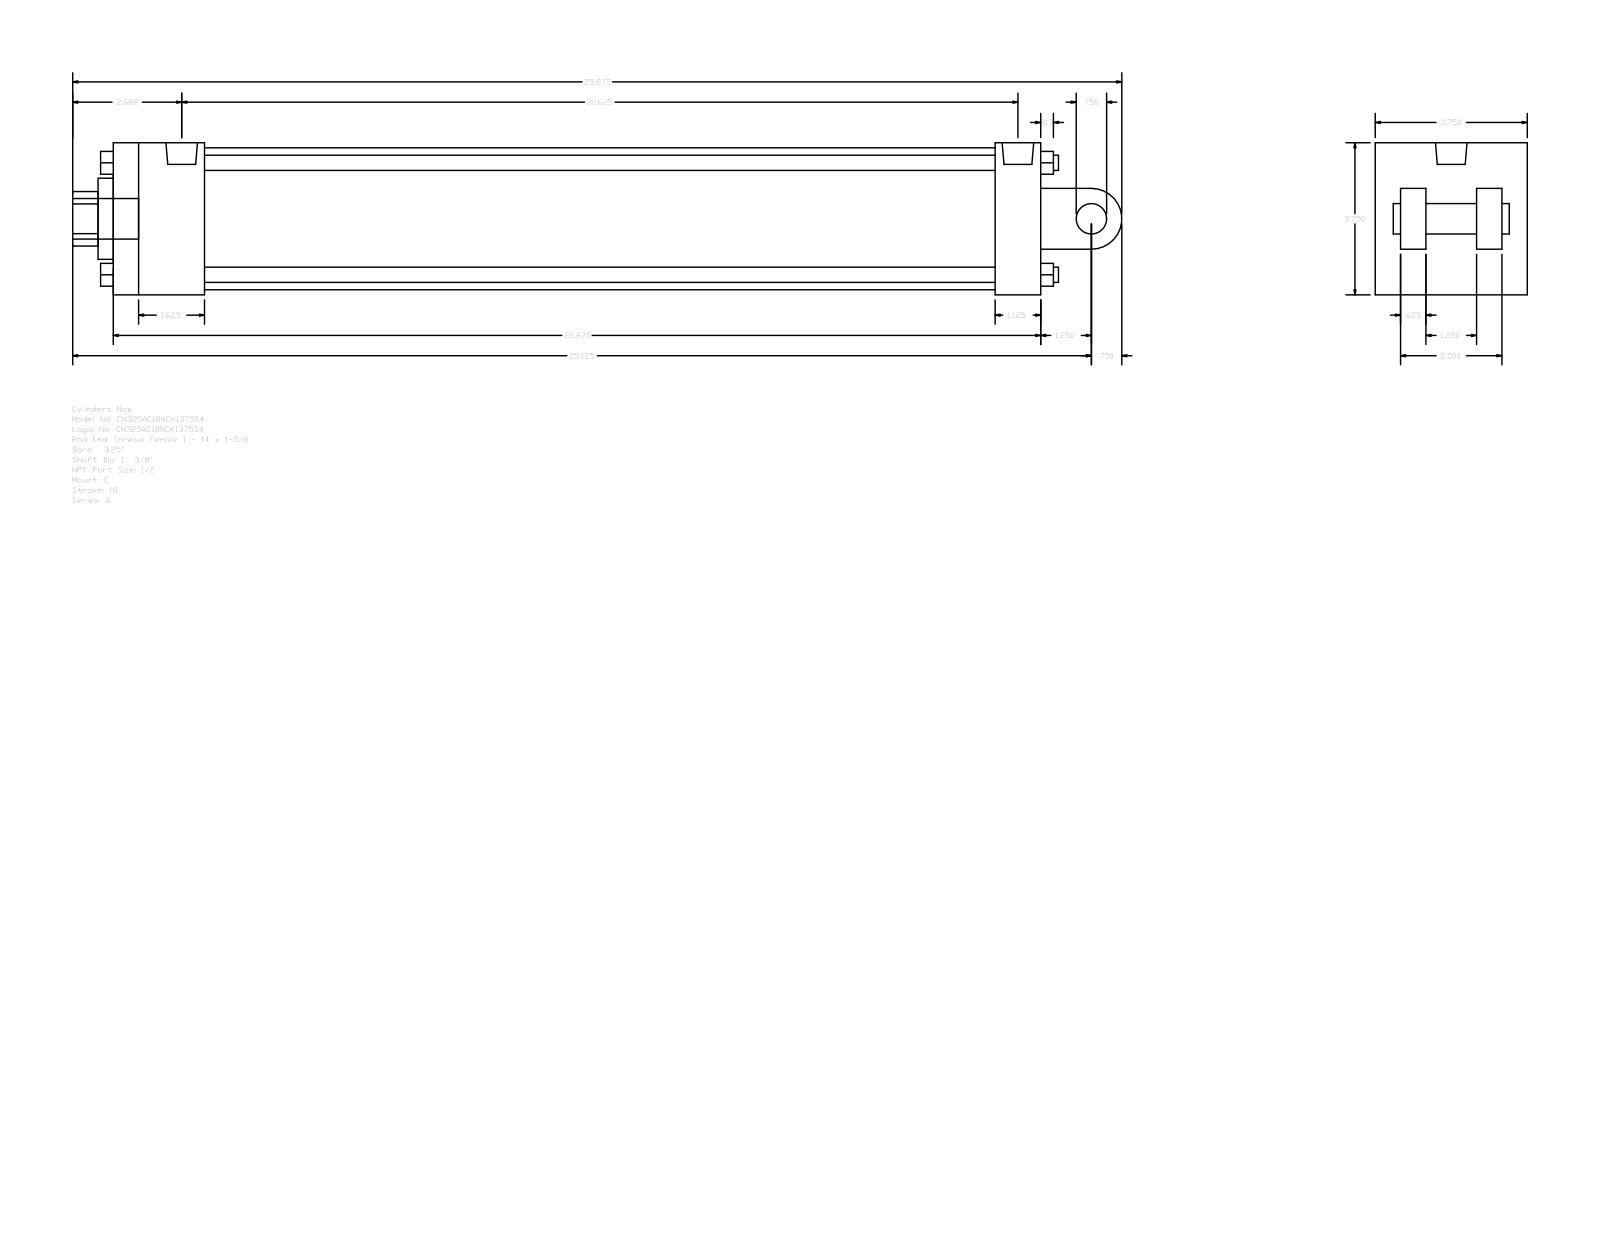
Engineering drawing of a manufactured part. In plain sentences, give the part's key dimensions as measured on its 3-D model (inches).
The part is named "A_C__0325_1.375". Its 3-D file was written by "GSSL Pune (CONFIG_CONTROL_DESIGN)". It is 0 solids with 135 faces: 102 planar, 33 cylindrical and 0 other. Overall it measures 25.875 by 3.75 by 3.75 inches. Round holes: 2 of diameter 0.344, 1 of diameter 0.778, 1 of diameter 1.375, 1 of diameter 2, 1 of diameter 3.5. Round bosses or shafts: 4 of diameter 0.375, 2 of diameter 0.344, 1 of diameter 1, 1 of diameter 0.778, 1 of diameter 0.75. Partial cylindrical surfaces (rounded edges, fillets, slot ends): 1 of radius 0.672, 1 of radius 0.75. The main face-to-face distances are 3.75, 0.625, 22.875, 1.125, 2.5, 2.625, 1.25, 3.125, 1.875, 21.75. The hole center spacings are 0.125.
